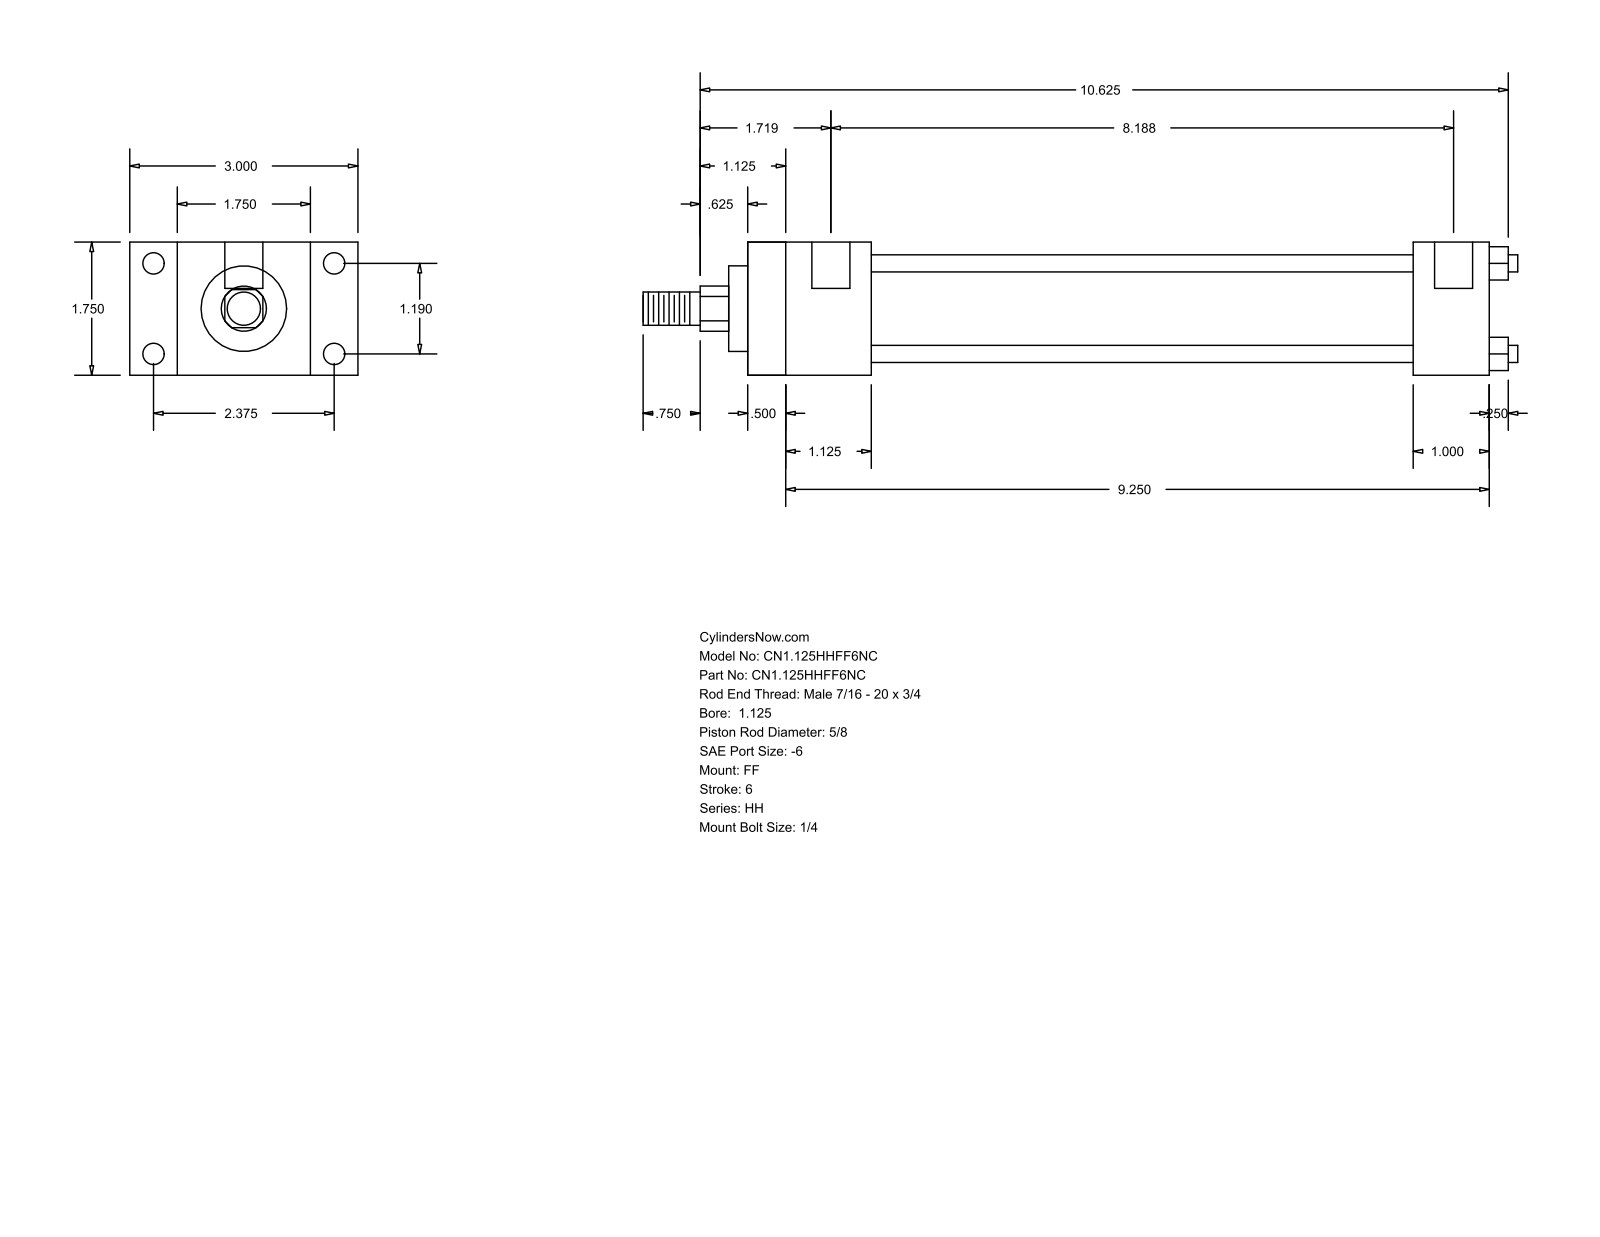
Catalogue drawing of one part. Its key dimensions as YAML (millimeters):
part_name: "HH_FF__0112_0.625"
step_written_by: "GSSL Pune (CONFIG_CONTROL_DESIGN)"
units: millimeters
bodies: {solids: 0, faces: 92, planar: 64, cylindrical: 28, other: 0}
overall_size: [292.1, 76.2, 44.45]
round_holes:
  - {diameter: 5.56, count: 4}
  - {diameter: 7.14, count: 4}
  - {diameter: 12.7, count: 2}
round_bosses_or_shafts:
  - {diameter: 5.71, count: 4}
  - {diameter: 34.92, count: 1}
  - {diameter: 28.57, count: 1}
  - {diameter: 15.88, count: 1}
  - {diameter: 11.11, count: 1}
partial_cylinders:
  - {radius: 7.54, count: 1}
face_to_face_distances: [44.46, 247.64, 15.87, 12.69, 234.95, 28.58, 60.33, 25.4, 41.27, 222.24]
hole_center_spacings: [30.22, 60.32, 67.47, 204.79, 3.17, 207.96]
